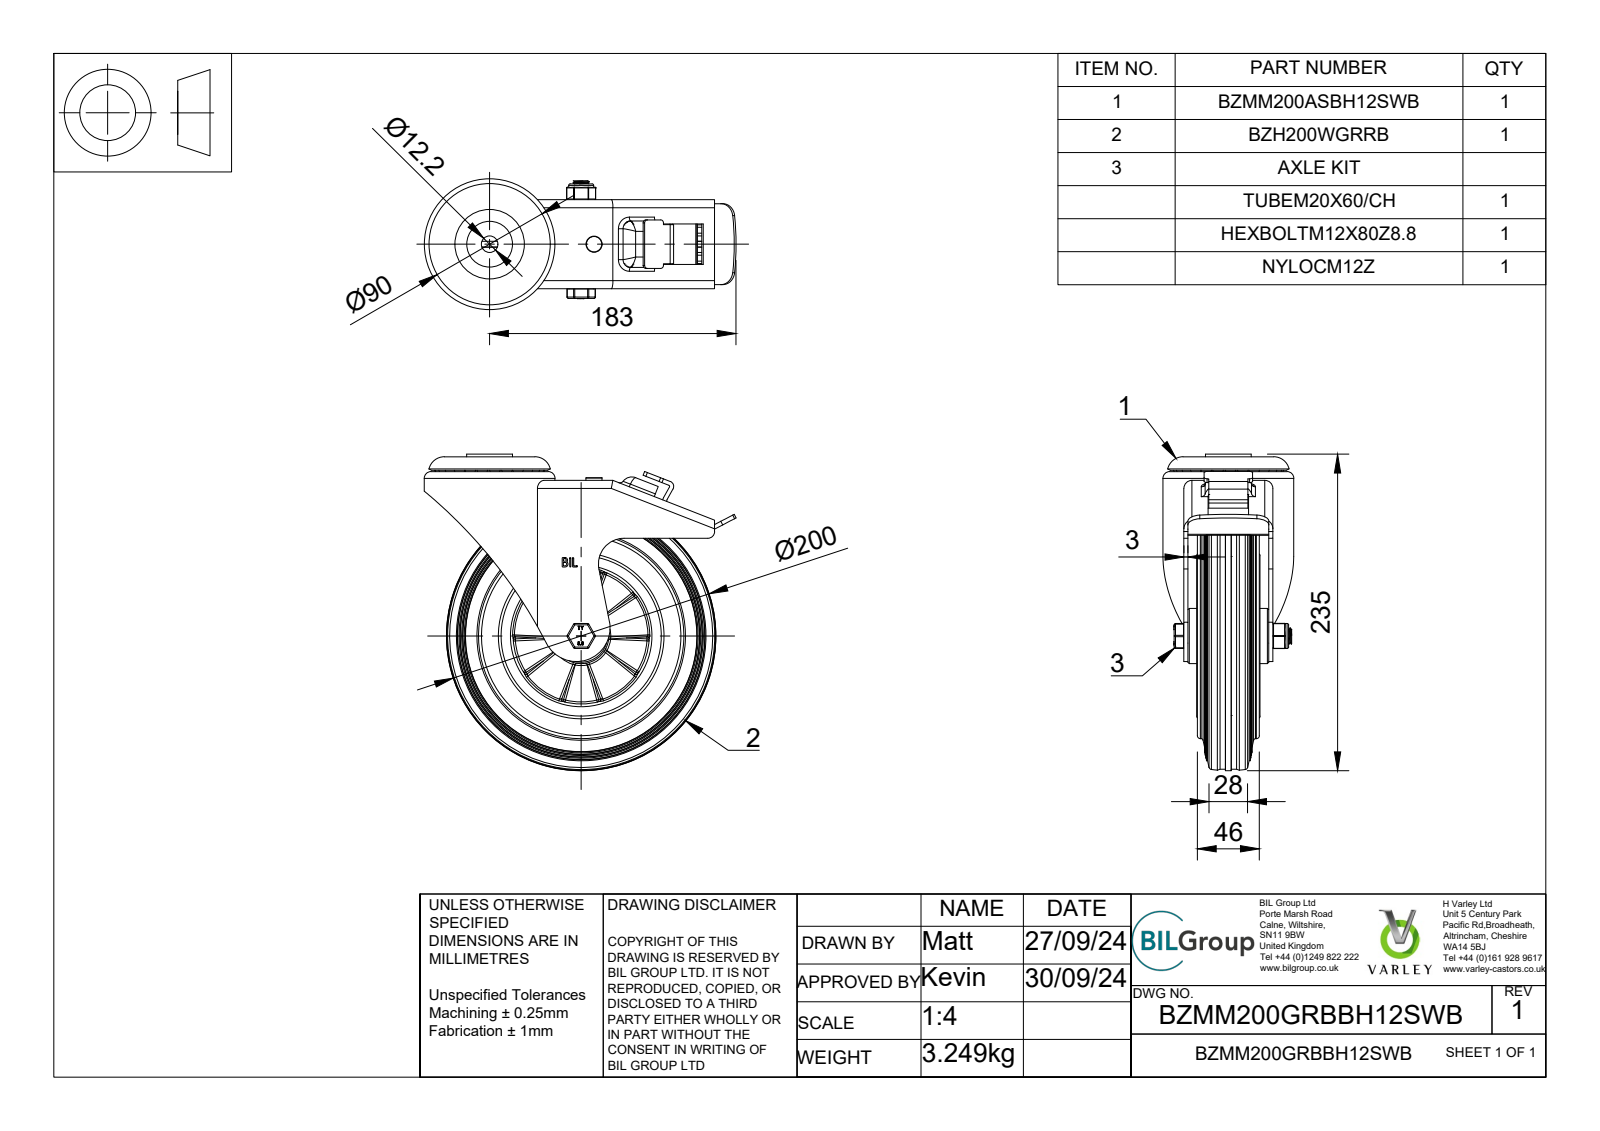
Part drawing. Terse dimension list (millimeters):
name: BZMM200GRBBH12SWB v3; BZMM200ASBH12SWB v1; ZINC PLATED, PRESSED STEEL HEAD; ZINC PLATED, PRESSED STEEL HEAD Geometry (+8 more)
written by: Autodesk Translation Framework v13.20.0.188 (AUTOMOTIVE_DESIGN)
unit: mm
bodies: 69 solids, 1164 faces (403 planar, 282 cylindrical, 479 other)
size: 235 × 231.5 × 97
volume: 1 221 000 mm³; area: 348 992 mm²
holes: 1× ⌀6, 1× ⌀7, 1× ⌀10, 1× ⌀12, 1× ⌀12.2, 1× ⌀12.3, 1× ⌀12.5, 1× ⌀14, 1× ⌀20, 1× ⌀35, 1× ⌀51, 1× ⌀58
bosses: 8× ⌀7.5, 2× ⌀34, 1× ⌀197.81, 1× ⌀152.5, 1× ⌀123, 1× ⌀97, 1× ⌀78, 1× ⌀41
rounds: 30× R1.5, 24× R0.5, 13× R1, 12× R0.25, 10× R0.75, 10× R2, 6× R3, 6× R3.25
face distances: 3, 63, 2.5, 6.5, 14, 49, 9.5, 60, 5, 12
hole spacings: 77.5
